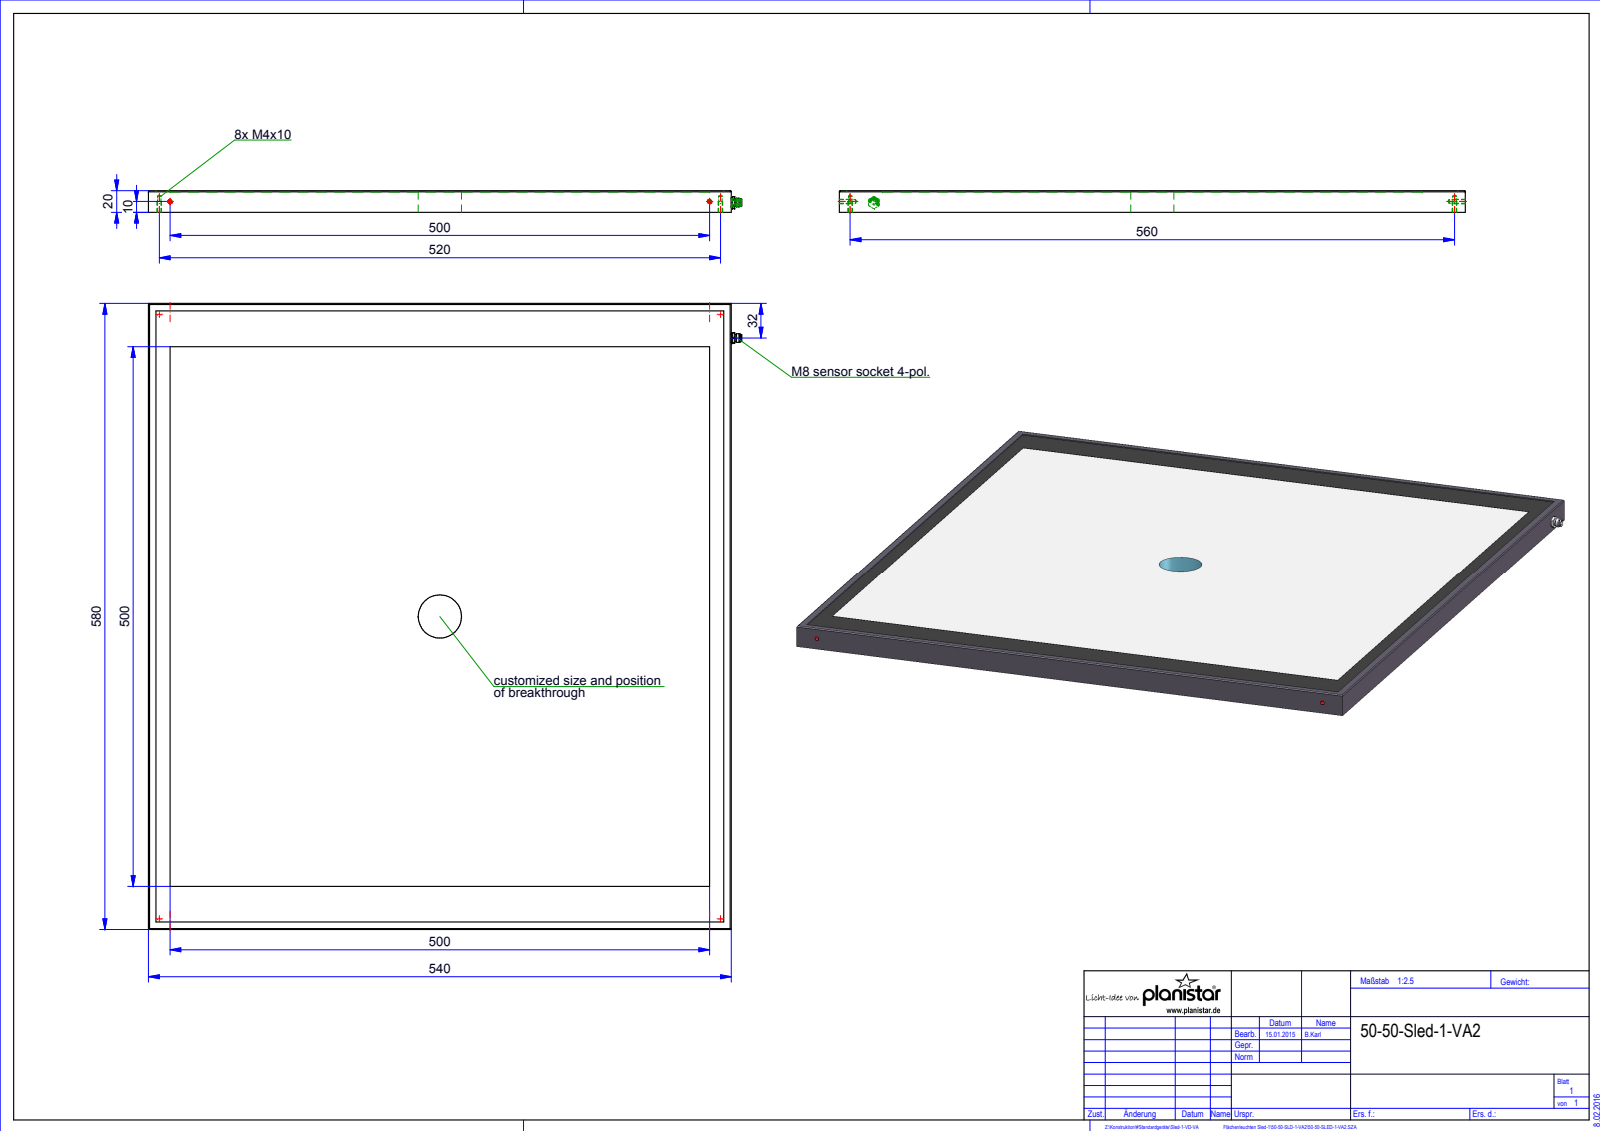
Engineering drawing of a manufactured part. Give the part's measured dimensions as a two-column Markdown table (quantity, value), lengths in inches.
| quantity | value |
| --- | --- |
| part name | Root; Baugruppe_Xled-2-VD; QUADER_0; 09-3391-00-04 |
| STEP written by | HiCAD 2015 2002.1 Build 408 (AUTOMOTIVE_DESIGN) |
| units | inches |
| bodies | 2 solids, 91 faces (36 planar, 38 cylindrical, 17 other) |
| overall size | 22.835 × 21.642 × 0.787 |
| volume | 359.5 in³ |
| surface area | 1 046 in² |
| round holes (diameter × count) | 0.13 × 6, 0.157 × 6, 0.228 × 1, 1.575 × 1 |
| round bosses / shafts (diameter × count) | 0.039 × 4, 0.315 × 1, 0.283 × 1, 0.268 × 1, 0.252 × 1 |
| partial cylindrical surfaces (radius × count) | 0.039 × 4, 0.217 × 1 |
| main face-to-face distances | 0.74, 0.748, 0.787, 0.047, 0.039, 21.26, 22.835, 0.276, 20.984, 22.559 |
| hole center spacings | 15.043, 20.472, 22.047, 30.087, 19.685 |
